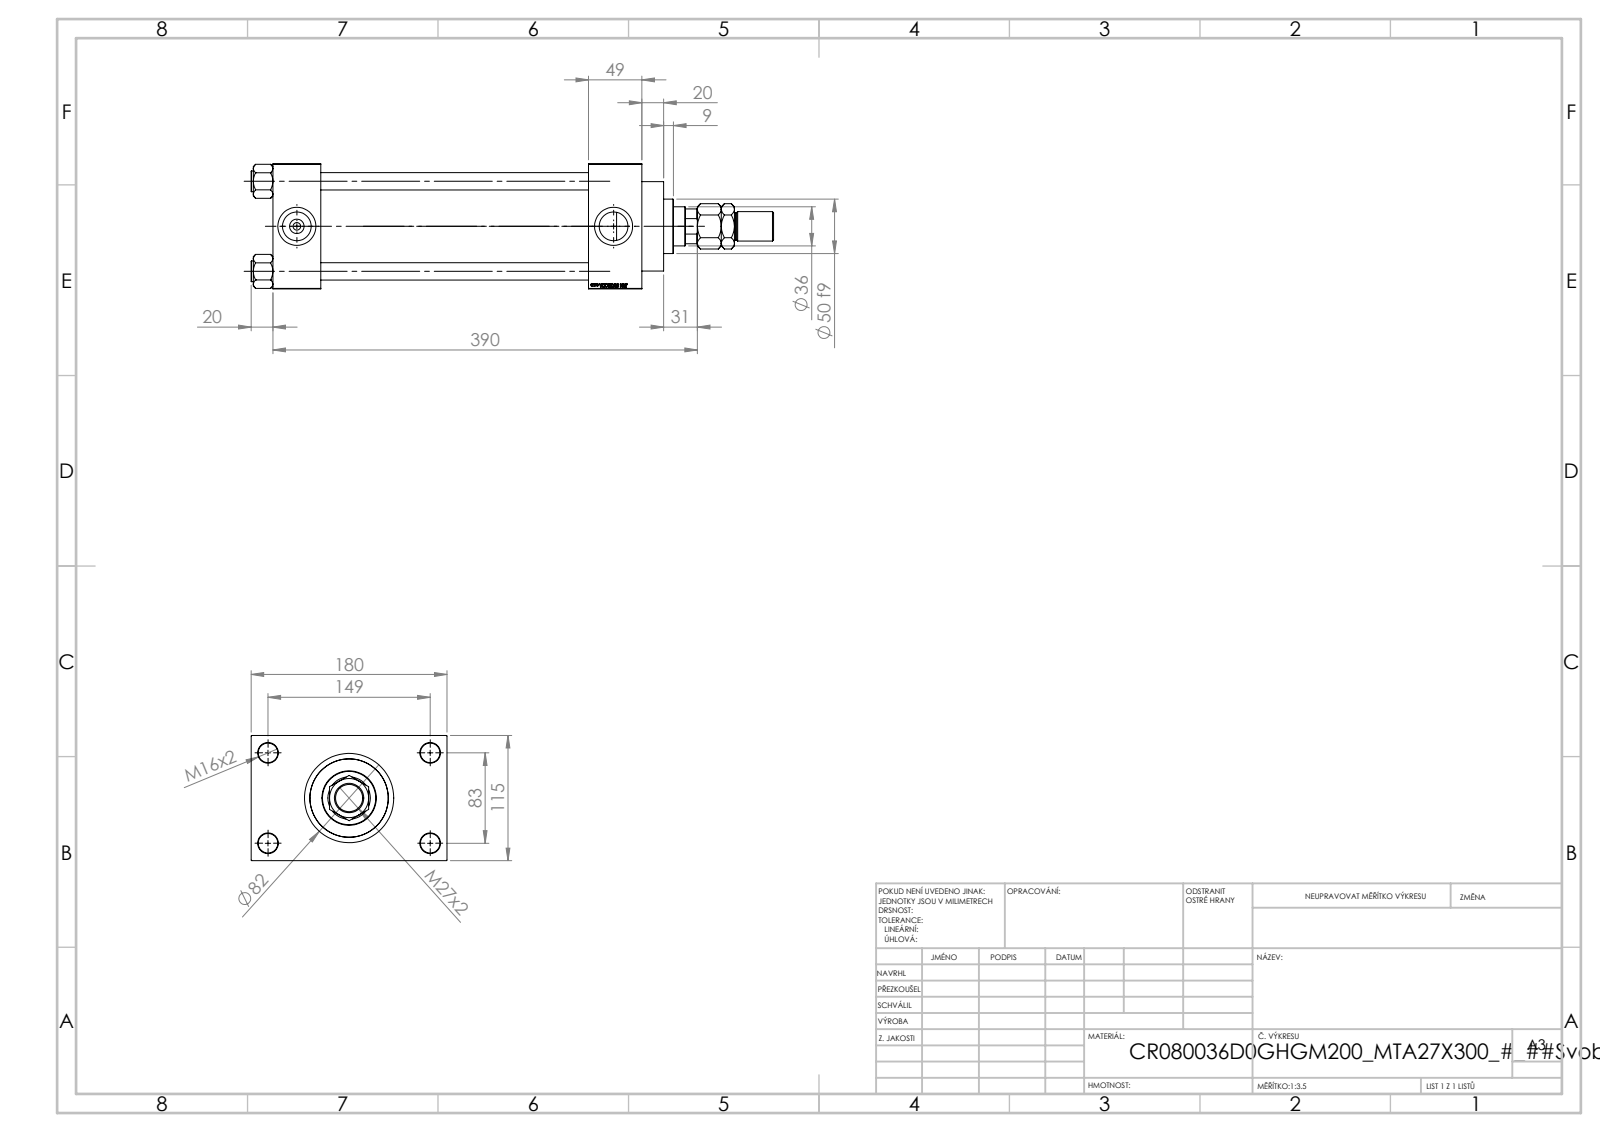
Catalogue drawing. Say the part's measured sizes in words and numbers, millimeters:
The part is named "V215CR_D_Body; V215CR_D_TYCINKA; V215_VC_A; V215CR_VCP_D (+2 more)". Its 3-D file was written by "SolidWorks 2019 (CONFIG_CONTROL_DESIGN)". It is 12 solids with 1200 faces: 560 planar, 92 cylindrical and 548 other. Overall it measures 480 by 180 by 115 millimeters. Its volume is 2 506 000 cubic millimeters and its surface area 456 473 square millimeters. Round holes: 4 of diameter 16, 4 of diameter 18, 2 of diameter 7, 2 of diameter 26.44, 2 of diameter 35, 1 of diameter 25.5, 1 of diameter 36, 1 of diameter 39, 1 of diameter 61, 1 of diameter 72, 1 of diameter 80. Round bosses or shafts: 4 of diameter 19, 1 of diameter 86, 1 of diameter 82, 1 of diameter 50, 1 of diameter 27, 1 of diameter 25. Partial cylindrical surfaces (rounded edges, fillets, slot ends): 1 of radius 17.5. The main face-to-face distances are 115, 246, 295, 49, 44, 290, 339, 32.5, 147.5, 180. The hole center spacings are 33.15, 58.48, 82.7, 85.28, 89.24, 115.85, 142.43, 83.
